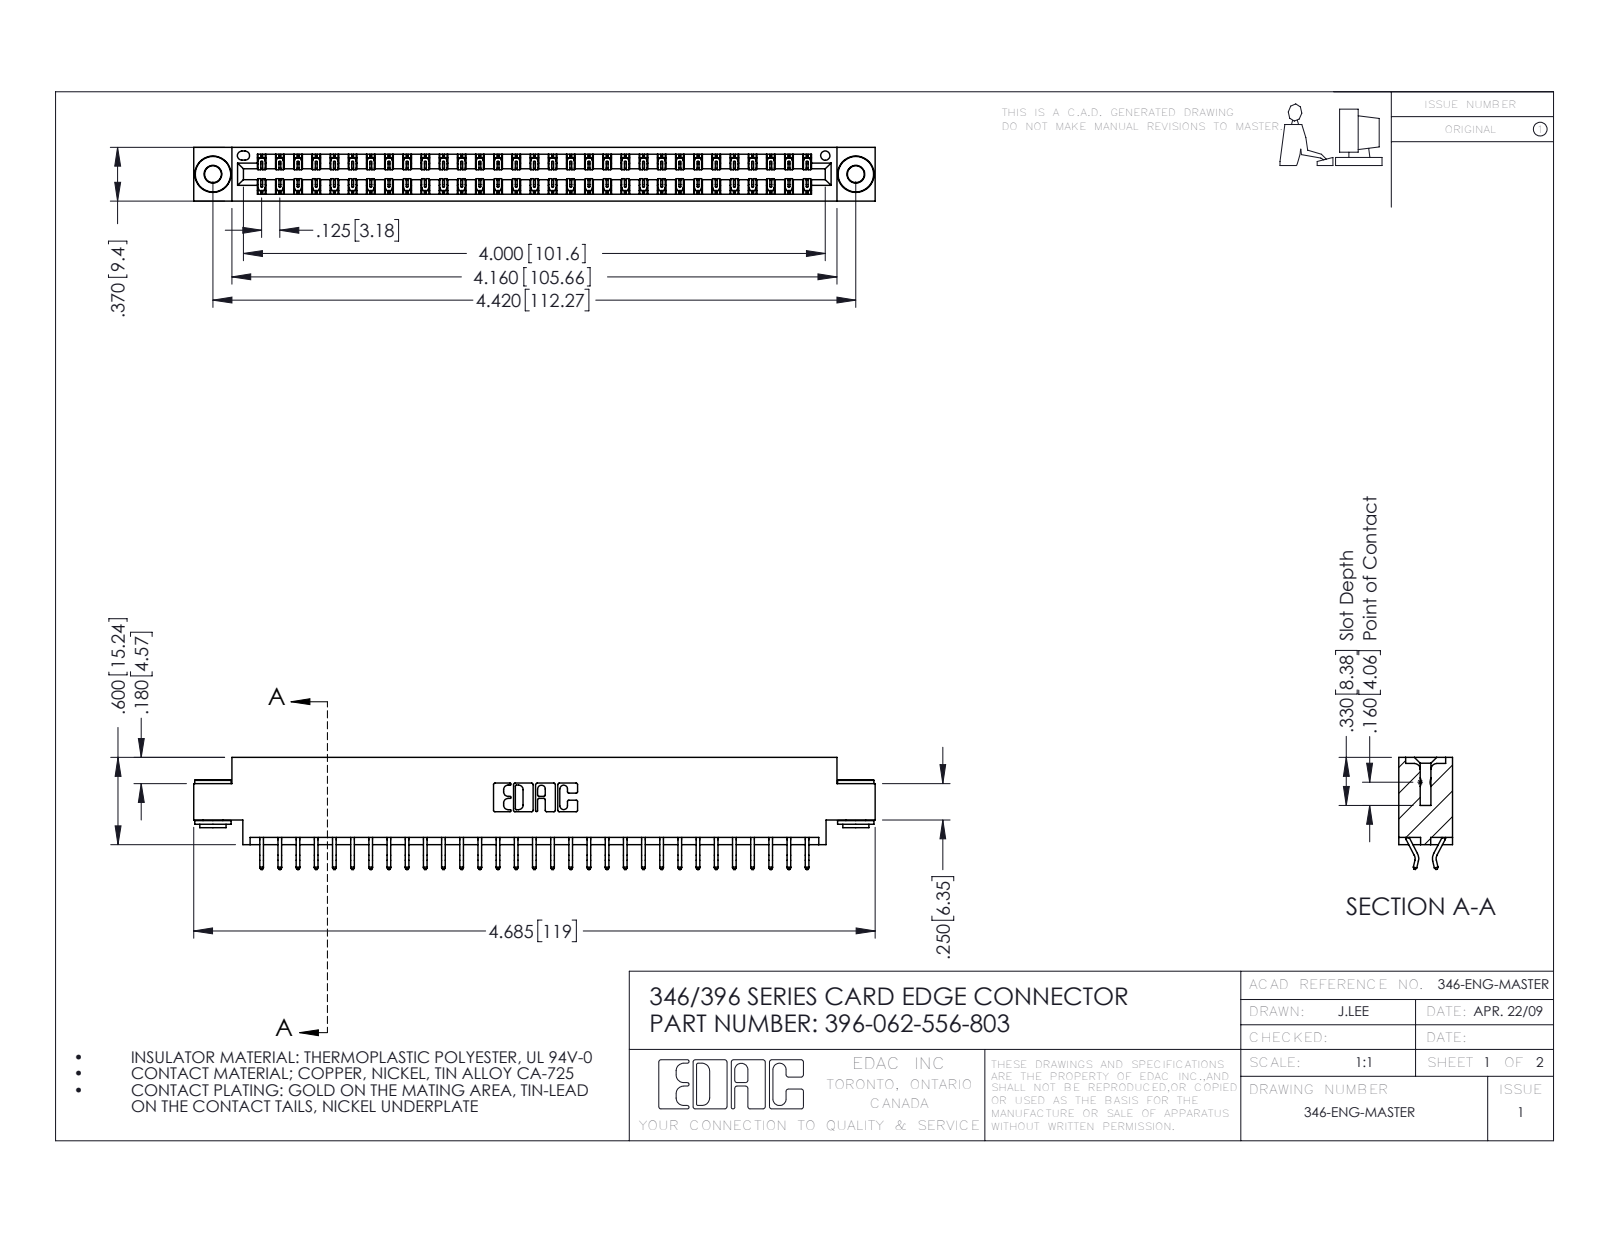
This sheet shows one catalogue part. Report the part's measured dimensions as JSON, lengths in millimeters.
{"part_name": "346 Part_0.170 Offset - 0.156 Dia-TH; 345-292-001_556 Tail; 345-250-002_345-250-002-102; 396-062-556-803", "step_written_by": "SolidWorks 2016 (CONFIG_CONTROL_DESIGN)", "units": "millimeters", "bodies": {"solids": 65, "faces": 3760, "planar": 2508, "cylindrical": 1244, "other": 8}, "overall_size": [119, 19.6, 9.4], "volume_mm3": 11400, "surface_area_mm2": 15810, "round_holes": [[2.9, 2], [4, 2], [1.6, 1]], "round_bosses_or_shafts": [[6.4, 2], [4.6, 2], [3.5, 2]], "partial_cylinders_radius": [[0.2, 93], [0.3, 22], [0.2, 6], [0.8, 6], [0.7, 3], [0.3, 2], [0.4, 2], [0.6, 2]], "face_to_face_distances": [1.2, 8.2, 9.4, 6.4, 0.6, 7, 1.8, 7.6, 3.8, 5.6], "hole_center_spacings": [6.2, 107, 112.3]}
